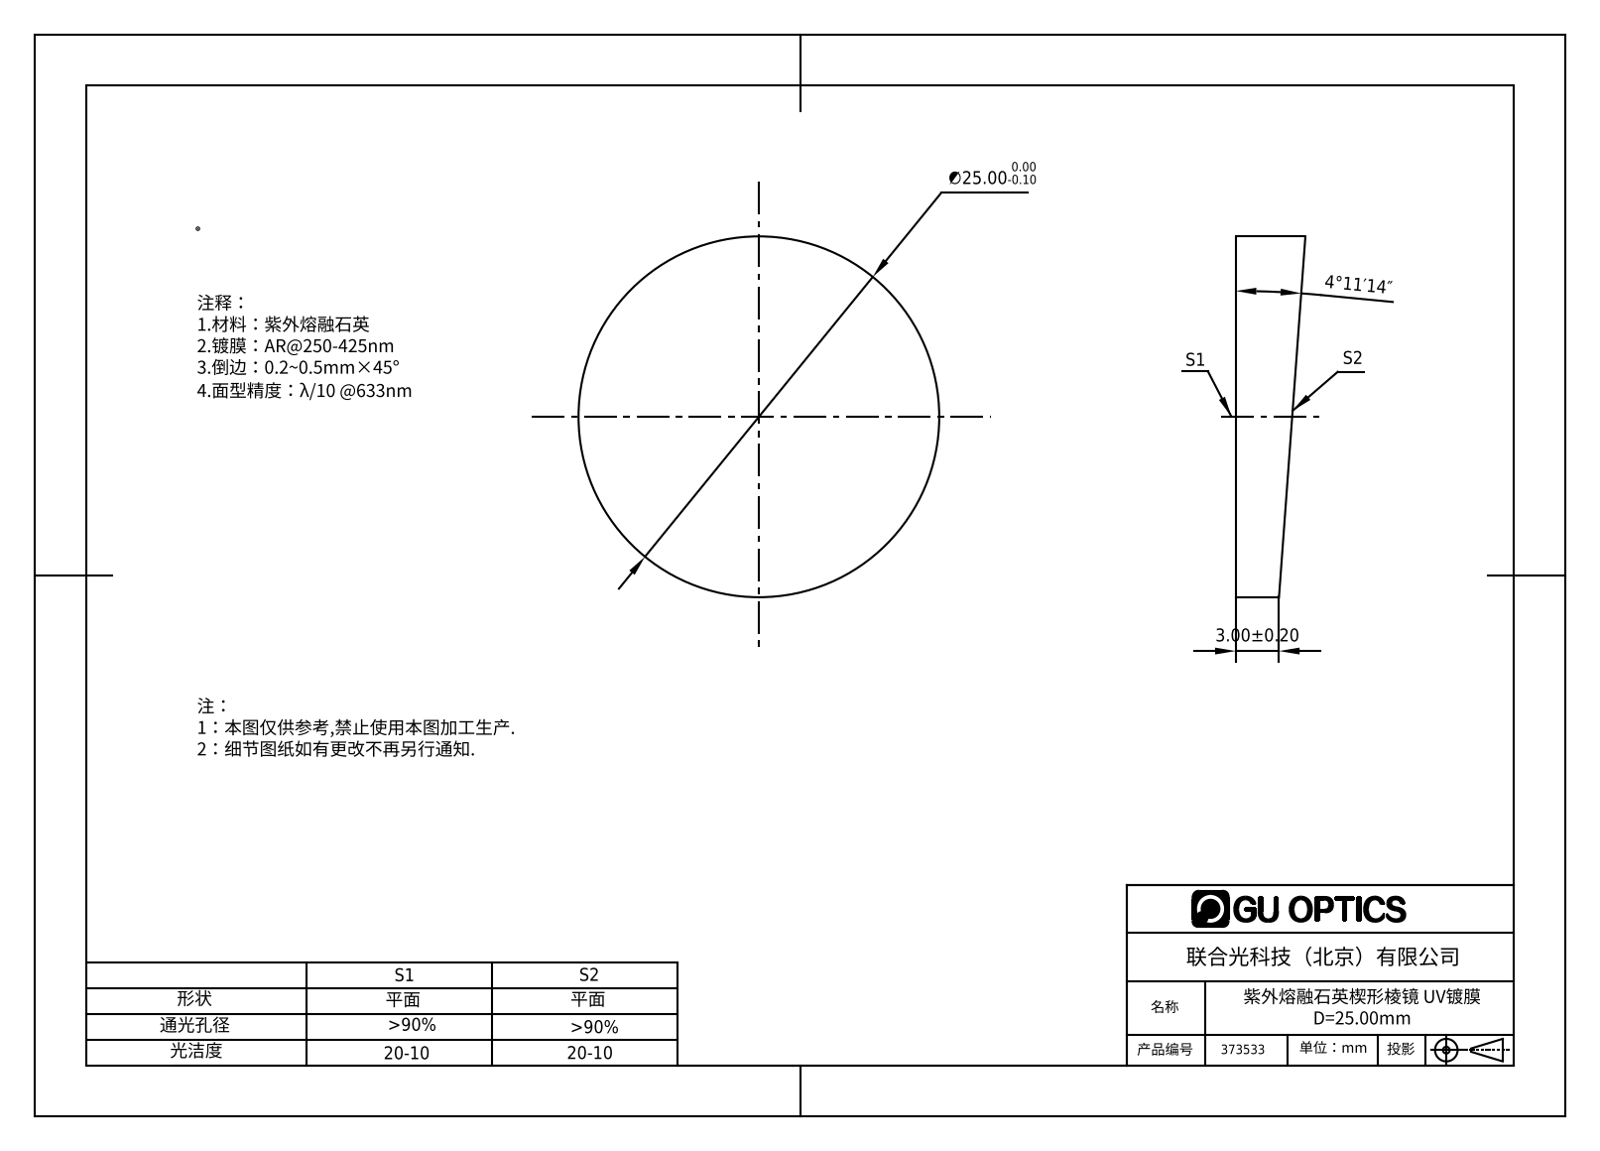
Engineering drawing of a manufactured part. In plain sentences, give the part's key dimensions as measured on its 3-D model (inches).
The part is named "373532". Its 3-D file was written by "SolidWorks 2016 (CONFIG_CONTROL_DESIGN)". It is 1 solid with 4 faces: 2 planar, 2 cylindrical and 0 other. Overall it measures 0.984 by 0.984 by 0.19 inches. Its volume is 0.117 cubic inches and its surface area 2.001 square inches. Round bosses or shafts: 1 of diameter 0.984.
